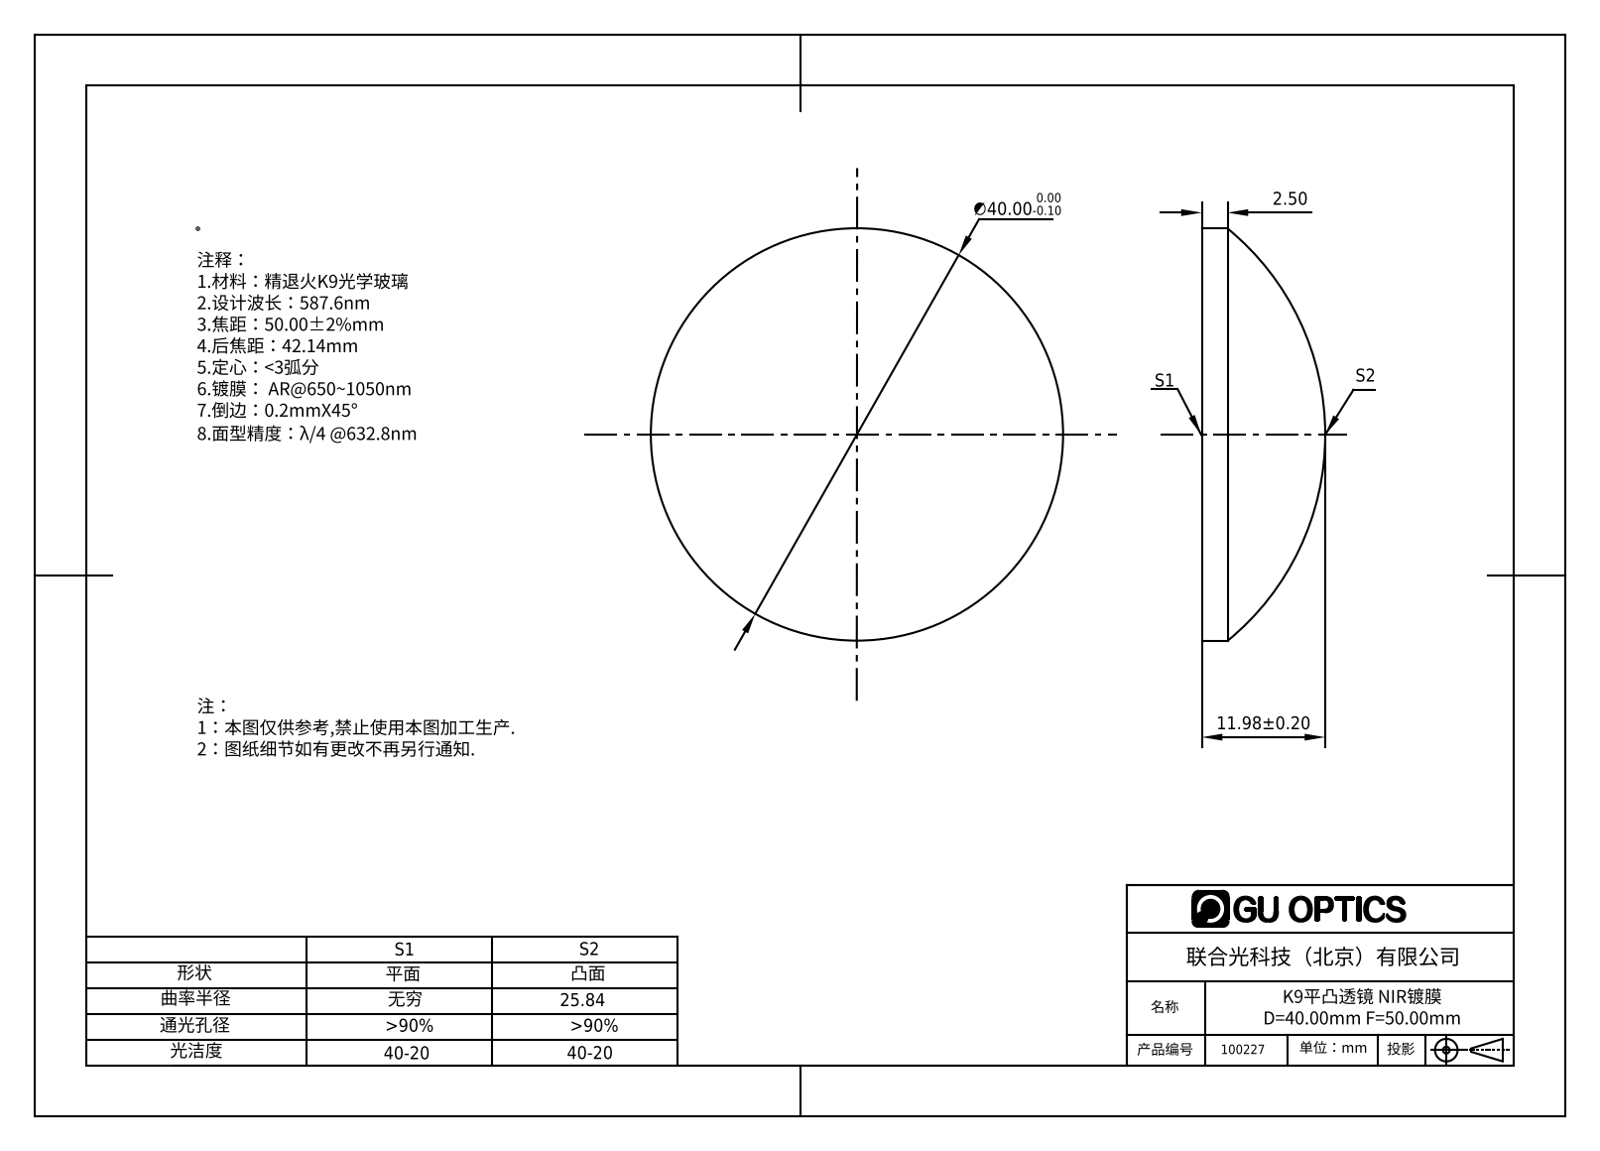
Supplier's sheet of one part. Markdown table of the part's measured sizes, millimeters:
| quantity | value |
| --- | --- |
| part name | 100227 |
| STEP written by | SolidWorks 2016 (AUTOMOTIVE_DESIGN) |
| units | millimeters |
| bodies | 1 solid, 5 faces (1 planar, 2 cylindrical, 2 other) |
| overall size | 40 × 40 × 11.98 |
| volume | 9 544 mm³ |
| surface area | 3 110 mm² |
| round bosses / shafts (diameter × count) | 40 × 1 |
